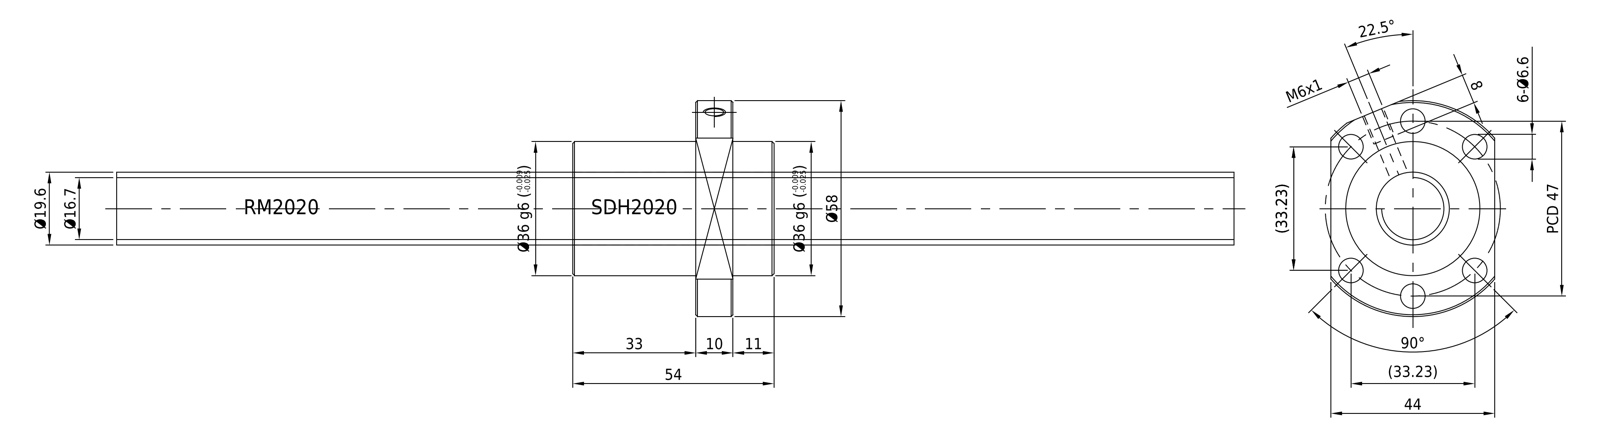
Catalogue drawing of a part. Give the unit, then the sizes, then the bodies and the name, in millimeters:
Units: millimetres
Overall size (bounding box): 300 × 57.99 × 44
Round holes (diameter × count): ⌀6.6 ×6, ⌀3 ×1, ⌀5 ×1, ⌀20 ×1
Round bosses / shafts (diameter × count): ⌀36 ×1, ⌀19.6 ×1
Partial cylindrical surfaces — rounded edges, fillets, slot ends (radius × count): R29 ×2
Main face-to-face distances: 10, 11, 21, 54, 43, 33, 123, 177, 44, 134
Hole centre spacings: 23.5, 17.99, 33.23, 43.43, 47, 17.98, 23.49, 23.51
Volume: 138 588 mm³ · Surface area: 34 003 mm²
Bodies: 2 solids, 47 faces (9 planar, 28 cylindrical, 10 other)
Part name (STEP PRODUCT): SDH2020; RM2020
STEP written by: SolidWorks 2013 (CONFIG_CONTROL_DESIGN)
